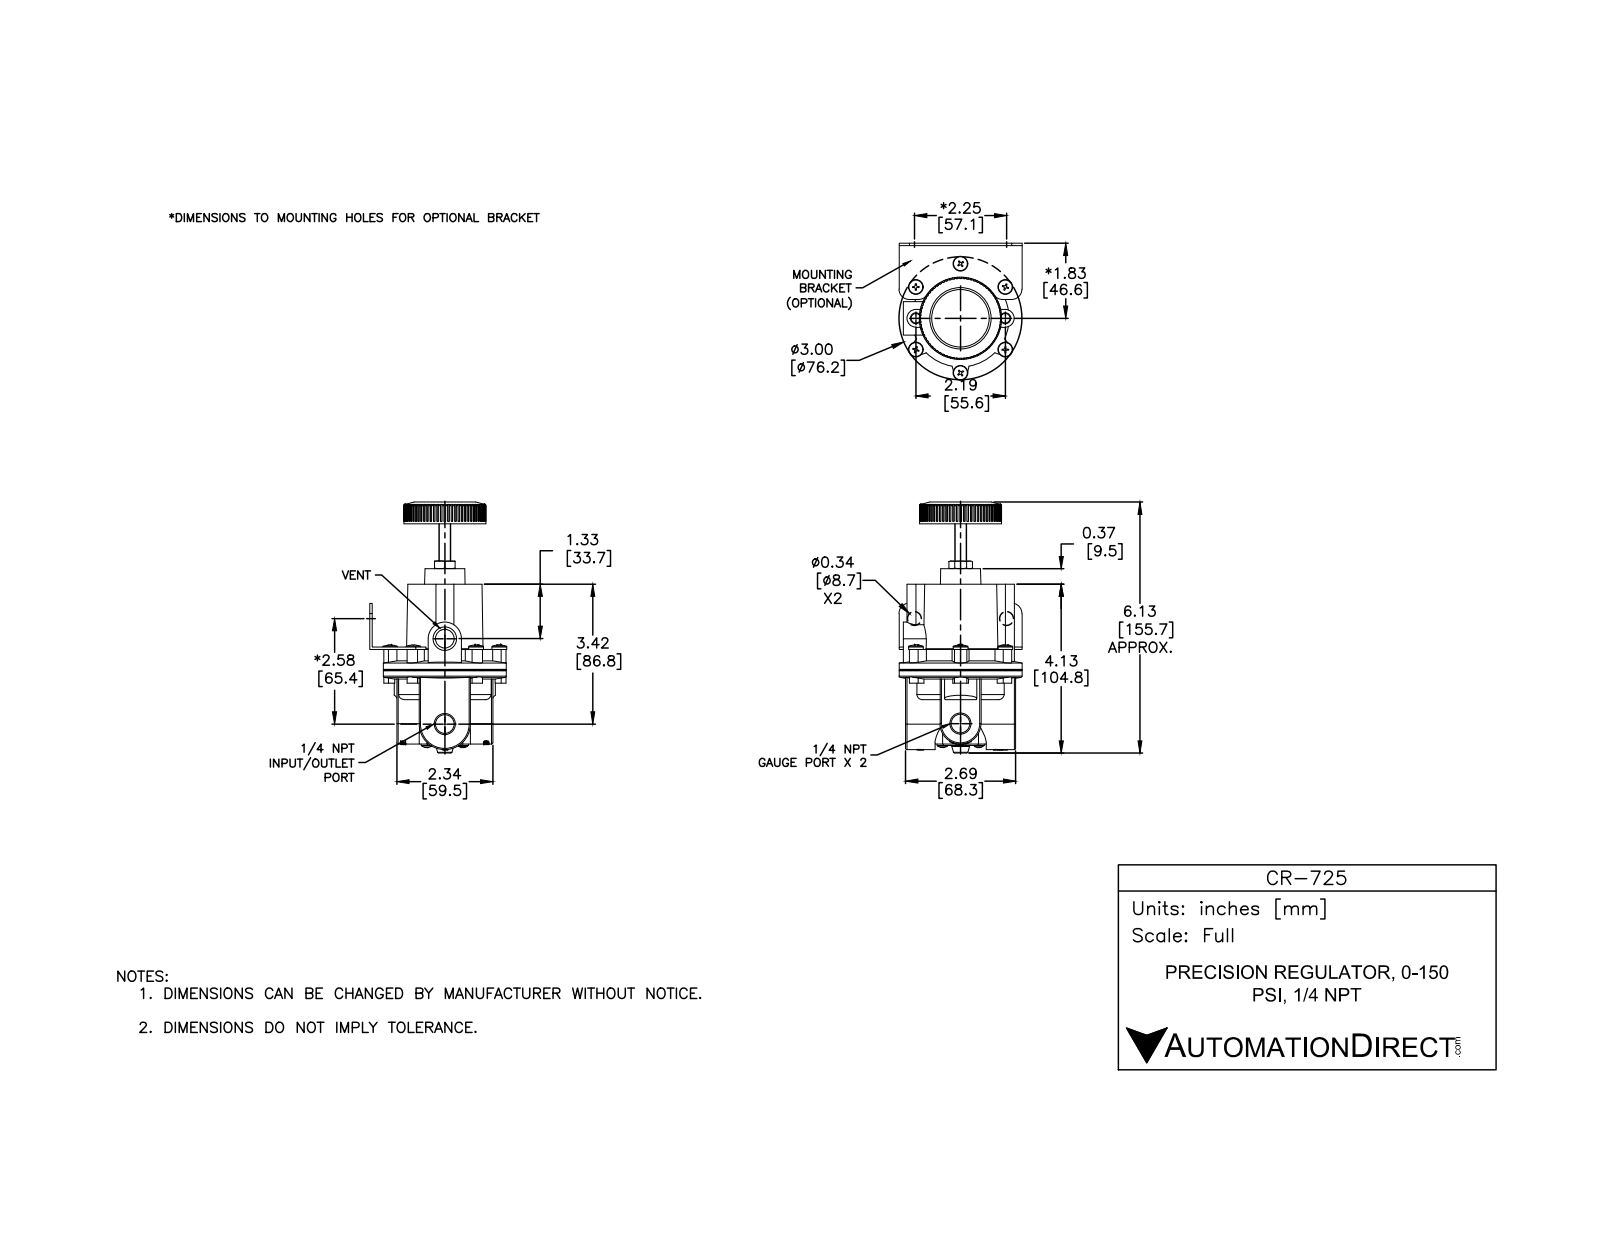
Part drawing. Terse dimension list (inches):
name: CR-725
written by: SolidWorks 2015 (CONFIG_CONTROL_DESIGN)
unit: in
bodies: 10 solids, 1525 faces (521 planar, 817 cylindrical, 187 other)
size: 6.123 × 3.041 × 3
volume: 17.48 in³; area: 87.7 in²
holes: 8× ⌀0.201, 6× ⌀0.159, 3× ⌀0.438, 1× ⌀1.403, 1× ⌀1.683
bosses: 6× ⌀0.373, 6× ⌀0.19, 6× ⌀0.149, 1× ⌀3, 1× ⌀2, 1× ⌀0.628, 1× ⌀0.281
rounds: 72× R0.004, 18× R0.02, 6× R0.032, 6× R0.156, 6× R0.157, 4× R0.141, 3× R0.187, 2× R0.033
face distances: 0.034, 2.114, 2.08, 0.524, 0.49, 1.59, 3.879, 3.845, 3.355, 1.765
hole spacings: 1.334, 1.725, 2.317, 0.765, 0.765, 1.094, 1.232, 1.232
